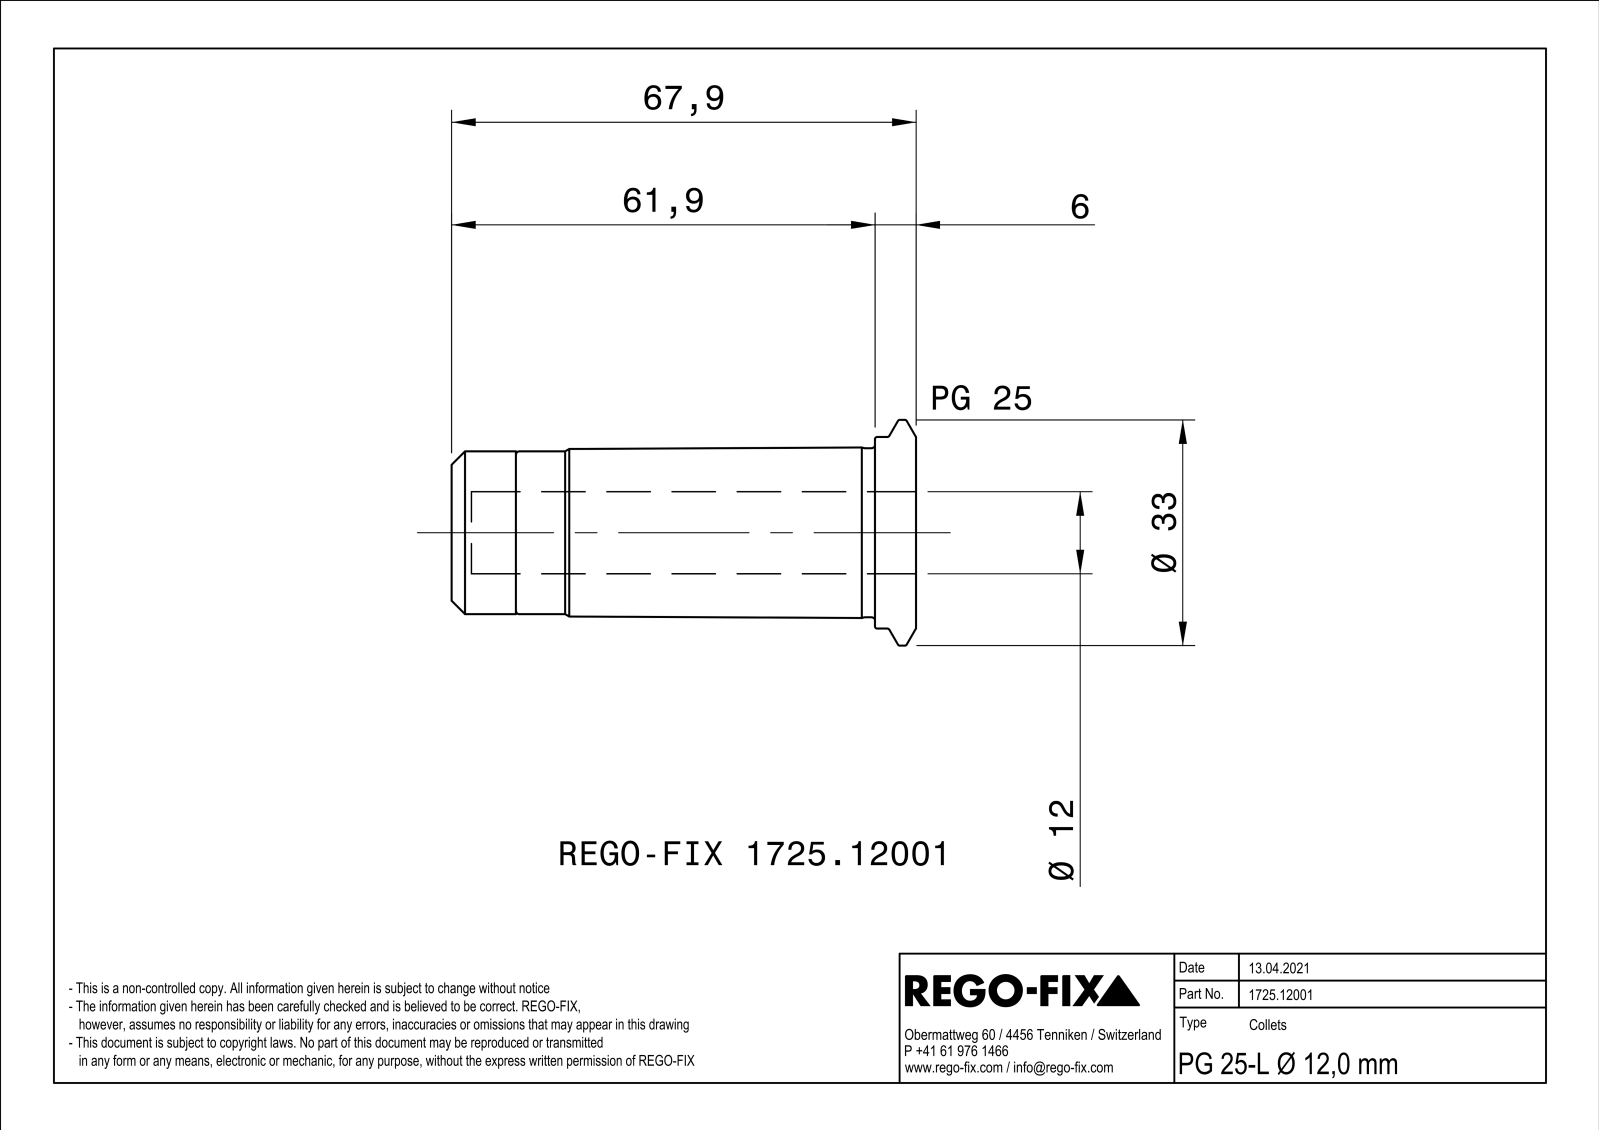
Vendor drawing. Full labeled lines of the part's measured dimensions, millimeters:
Part name (STEP PRODUCT): NOCUT
STEP written by: SIEMENS PLM Software Solid Edge ST10 (AUTOMOTIVE_DESIGN)
Units: millimetres
Bodies: 1 solid, 93 faces (29 planar, 21 cylindrical, 43 other)
Overall size (bounding box): 67.9 × 33 × 32.99
Round holes (diameter × count): ⌀2.8 ×1, ⌀12 ×1, ⌀18.5 ×1, ⌀20.4 ×1, ⌀22.2 ×1
Round bosses / shafts (diameter × count): ⌀33 ×1, ⌀28 ×1, ⌀24.7 ×1, ⌀23.8 ×1, ⌀22 ×1, ⌀20.92 ×1
Partial cylindrical surfaces — rounded edges, fillets, slot ends (radius × count): R2 ×3
Main face-to-face distances: 1, 67.9, 51, 16.9, 6, 52.5, 45, 61.9, 58.5, 7.5
